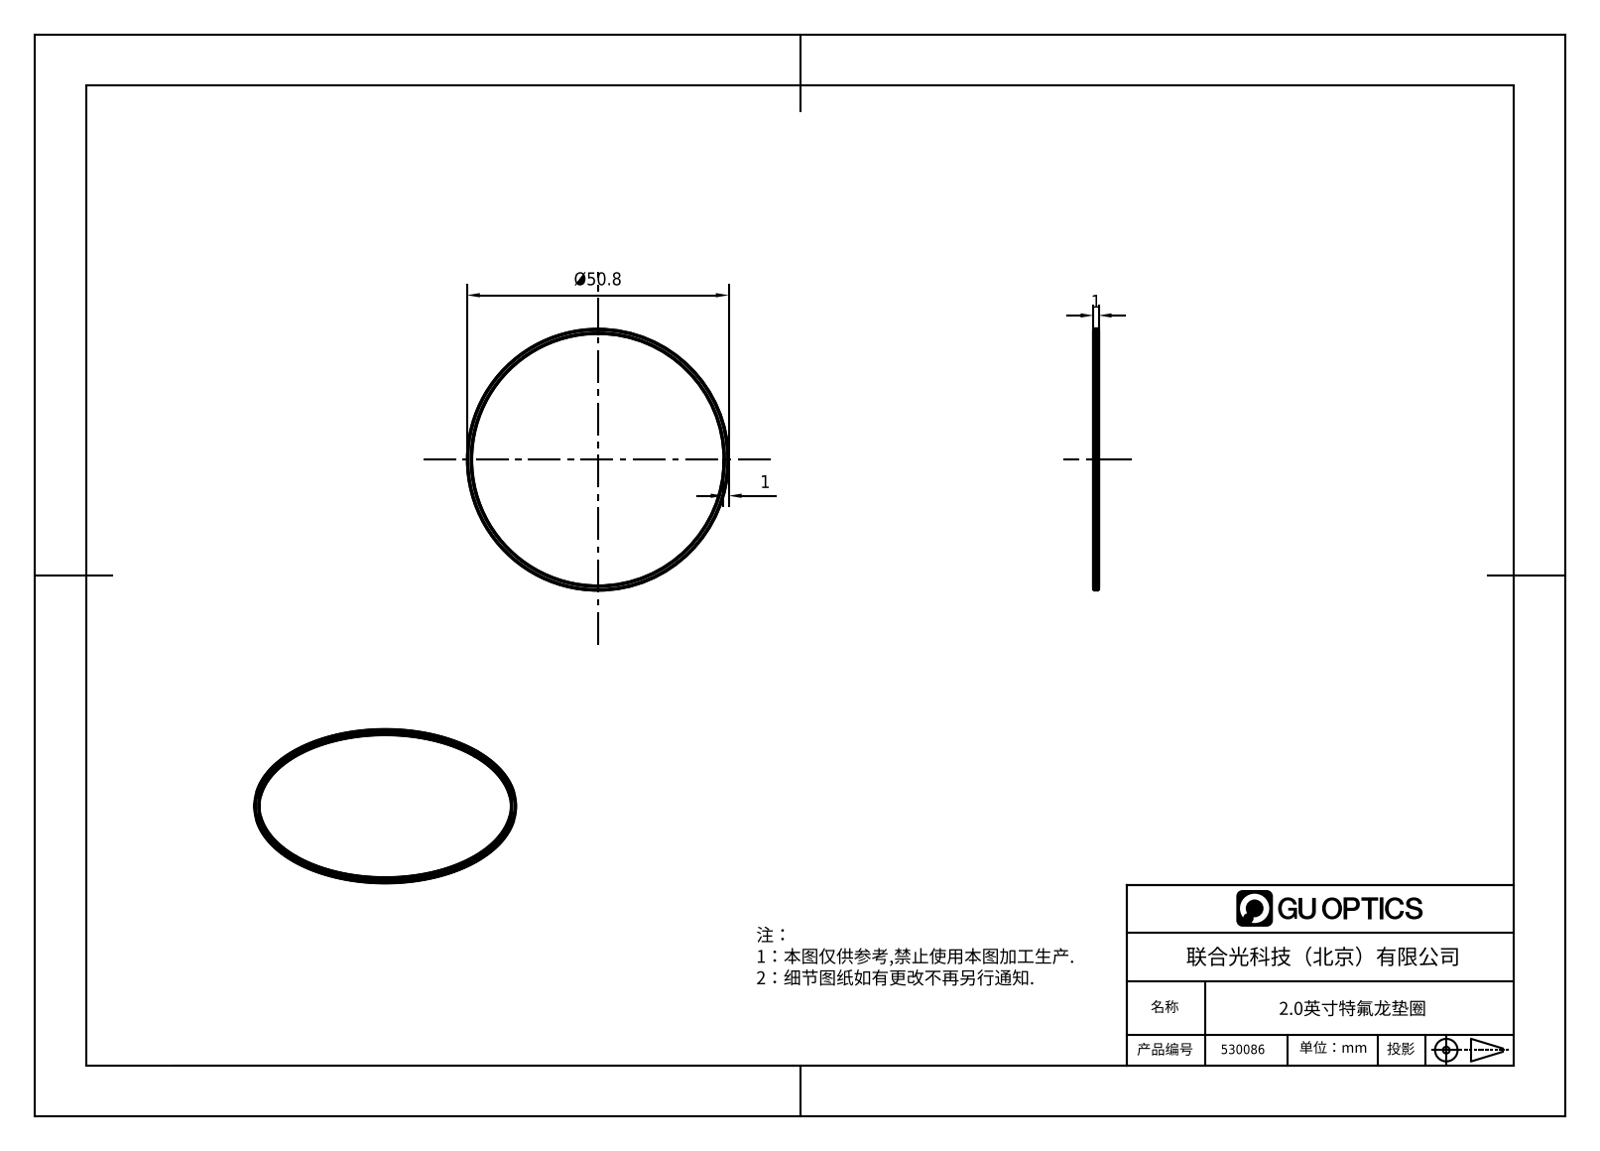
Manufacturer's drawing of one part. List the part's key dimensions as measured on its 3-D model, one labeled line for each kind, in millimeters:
Part name (STEP PRODUCT): 1.8.5.25_ZFK-D2.0_2.0英寸特氟龙垫圈
STEP written by: SolidWorks 2018 (CONFIG_CONTROL_DESIGN)
Units: millimetres
Bodies: 1 solid, 14 faces (2 planar, 4 cylindrical, 8 other)
Overall size (bounding box): 50.8 × 50.8 × 1
Volume: 148 mm³ · Surface area: 559 mm²
Round holes (diameter × count): ⌀48.8 ×1
Round bosses / shafts (diameter × count): ⌀50.8 ×1
Main face-to-face distances: 1
